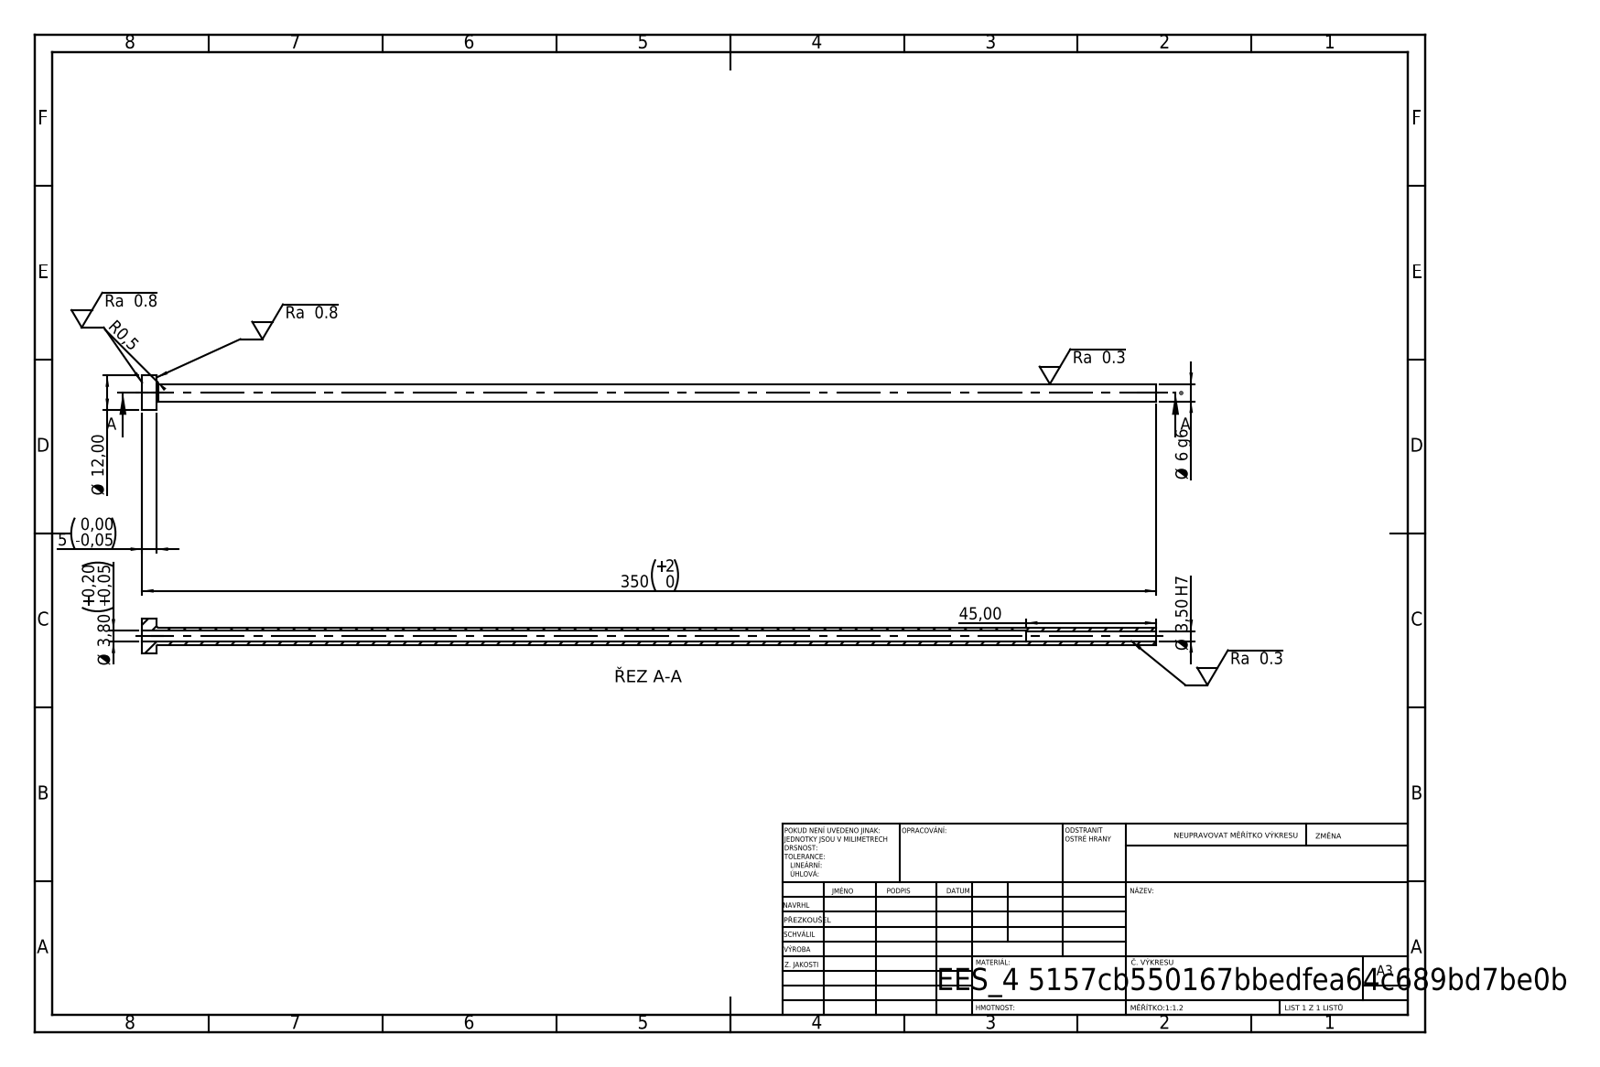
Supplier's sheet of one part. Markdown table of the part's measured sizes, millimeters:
| quantity | value |
| --- | --- |
| STEP written by | SolidWorks 2019 (CONFIG_CONTROL_DESIGN) |
| units | millimeters |
| bodies | 1 solid, 14 faces (4 planar, 8 cylindrical, 2 other) |
| overall size | 350 × 12 × 12 |
| volume | 6 429 mm³ |
| surface area | 11 031 mm² |
| round holes (diameter × count) | 3.5 × 1, 3.8 × 1 |
| round bosses / shafts (diameter × count) | 12 × 1, 6 × 1 |
| main face-to-face distances | 5, 350, 345, 305, 300, 45 |
